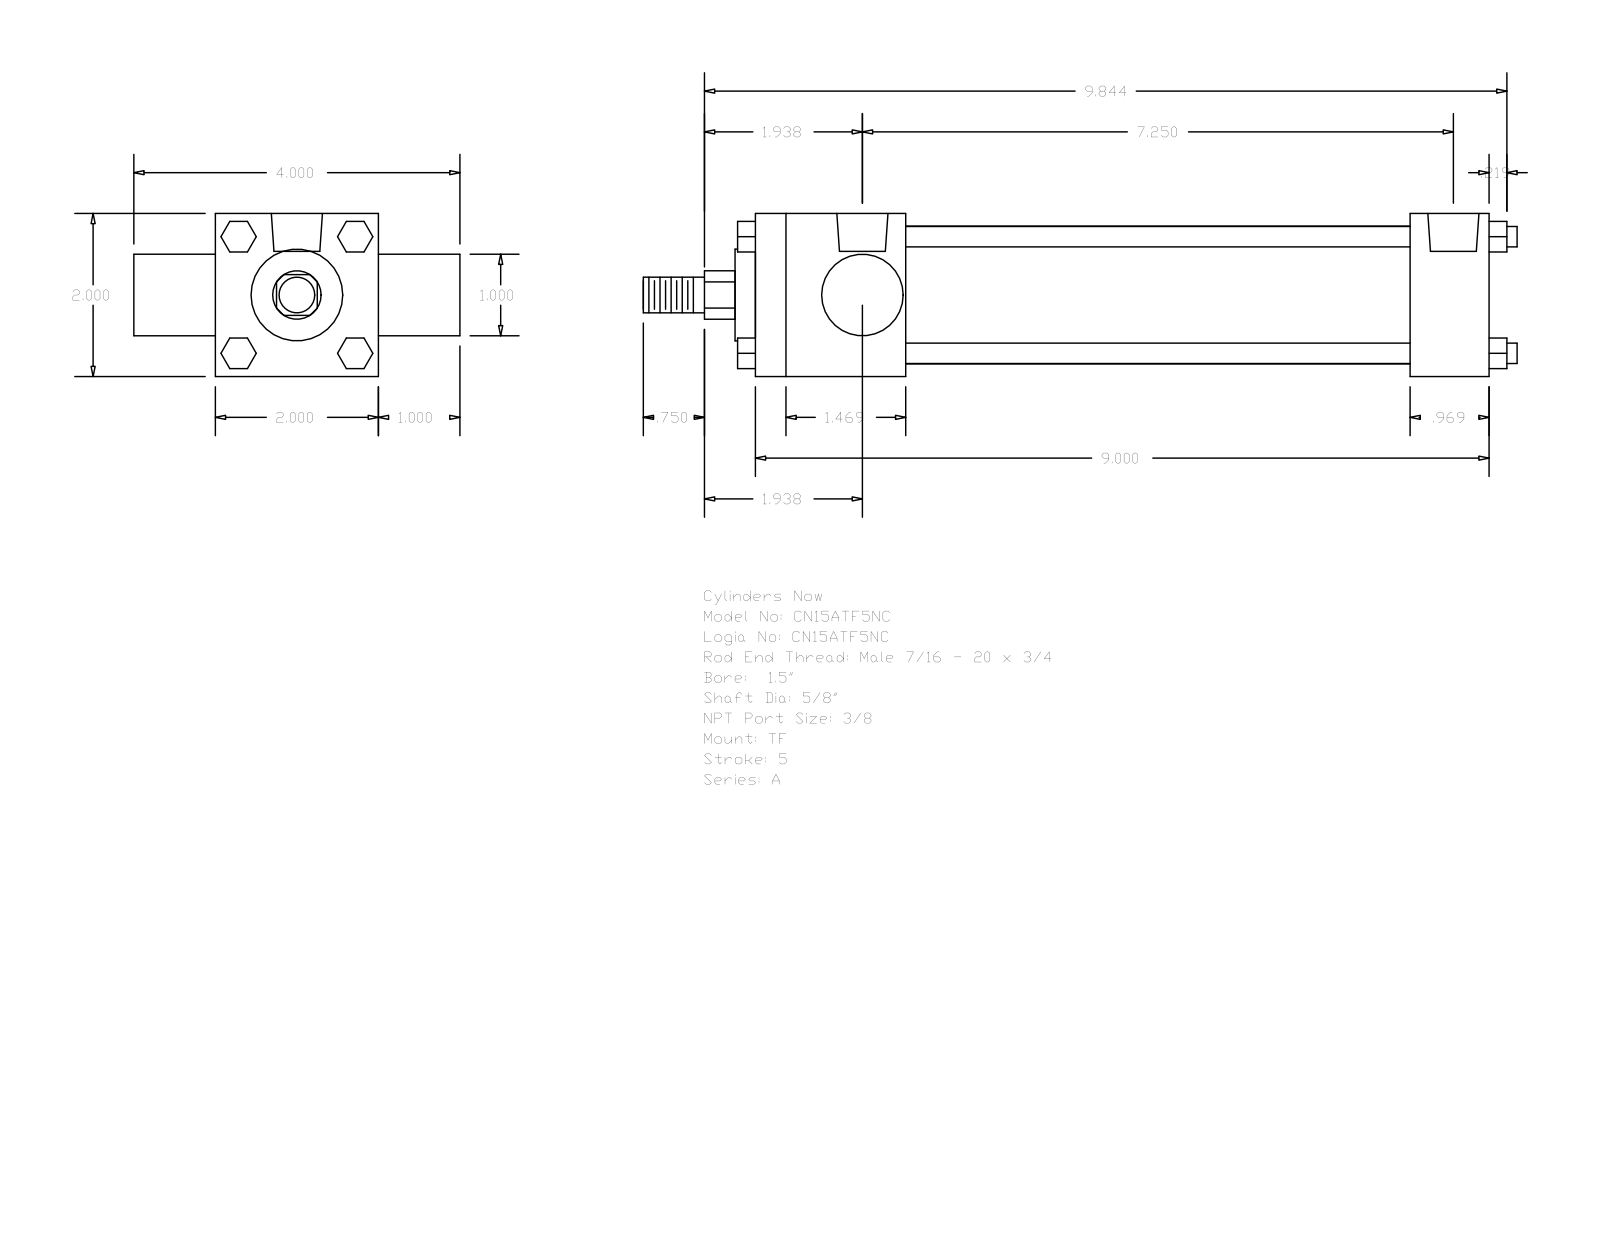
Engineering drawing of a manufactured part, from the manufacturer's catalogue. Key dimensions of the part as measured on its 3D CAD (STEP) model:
Part name (STEP PRODUCT): A_TF__0150_0.625
STEP written by: GSSL Pune (CONFIG_CONTROL_DESIGN)
Units: millimetres
Bodies: 0 solids, 120 faces (92 planar, 28 cylindrical, 0 other)
Overall size (bounding box): 272.26 × 101.6 × 50.8
Round holes (diameter × count): ⌀5.56 ×3, ⌀15.93 ×2
Round bosses / shafts (diameter × count): ⌀6.35 ×4, ⌀42.93 ×1, ⌀28.57 ×1, ⌀25.4 ×1, ⌀15.88 ×1, ⌀11.11 ×1
Partial cylindrical surfaces — rounded edges, fillets, slot ends (radius × count): R7.54 ×1
Main face-to-face distances: 50.8, 228.59, 25.4, 76.2, 46.83, 203.99, 157.16, 181.76, 24.6, 101.6
Hole centre spacings: 3.97, 180.18, 176.21, 184.15
